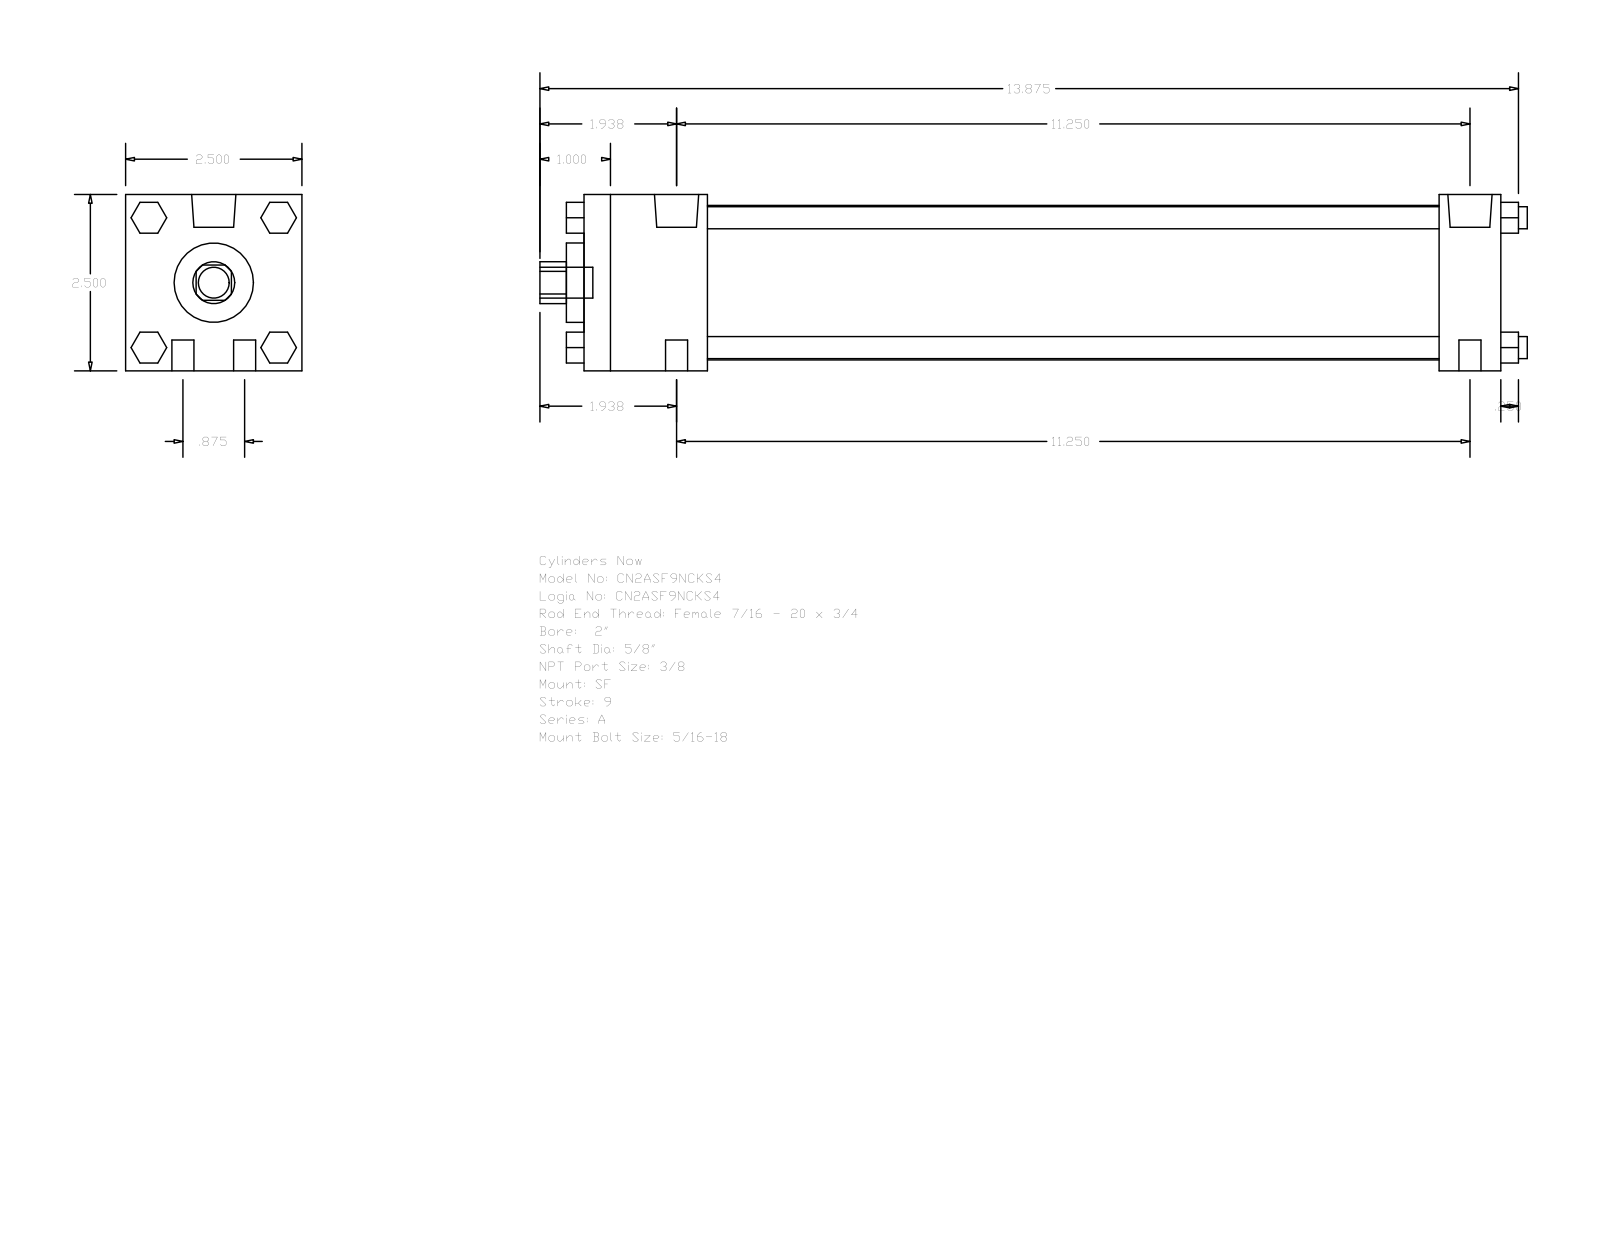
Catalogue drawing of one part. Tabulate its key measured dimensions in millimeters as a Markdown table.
| quantity | value |
| --- | --- |
| part name | A_SF__0200_0.625 |
| STEP written by | GSSL Pune (CONFIG_CONTROL_DESIGN) |
| units | millimeters |
| bodies | 0 solids, 124 faces (94 planar, 30 cylindrical, 0 other) |
| overall size | 355.6 × 63.5 × 63.5 |
| round holes (diameter × count) | 15.88 × 1, 28.57 × 1, 55.63 × 1 |
| round bosses / shafts (diameter × count) | 7.94 × 8, 15.93 × 2, 5.56 × 2, 11.11 × 1 |
| partial cylindrical surfaces (radius × count) | 7.54 × 1 |
| main face-to-face distances | 63.5, 330.19, 307.97, 22.22, 44.45, 263.52, 285.74, 50.8, 6.35, 314.32 |
